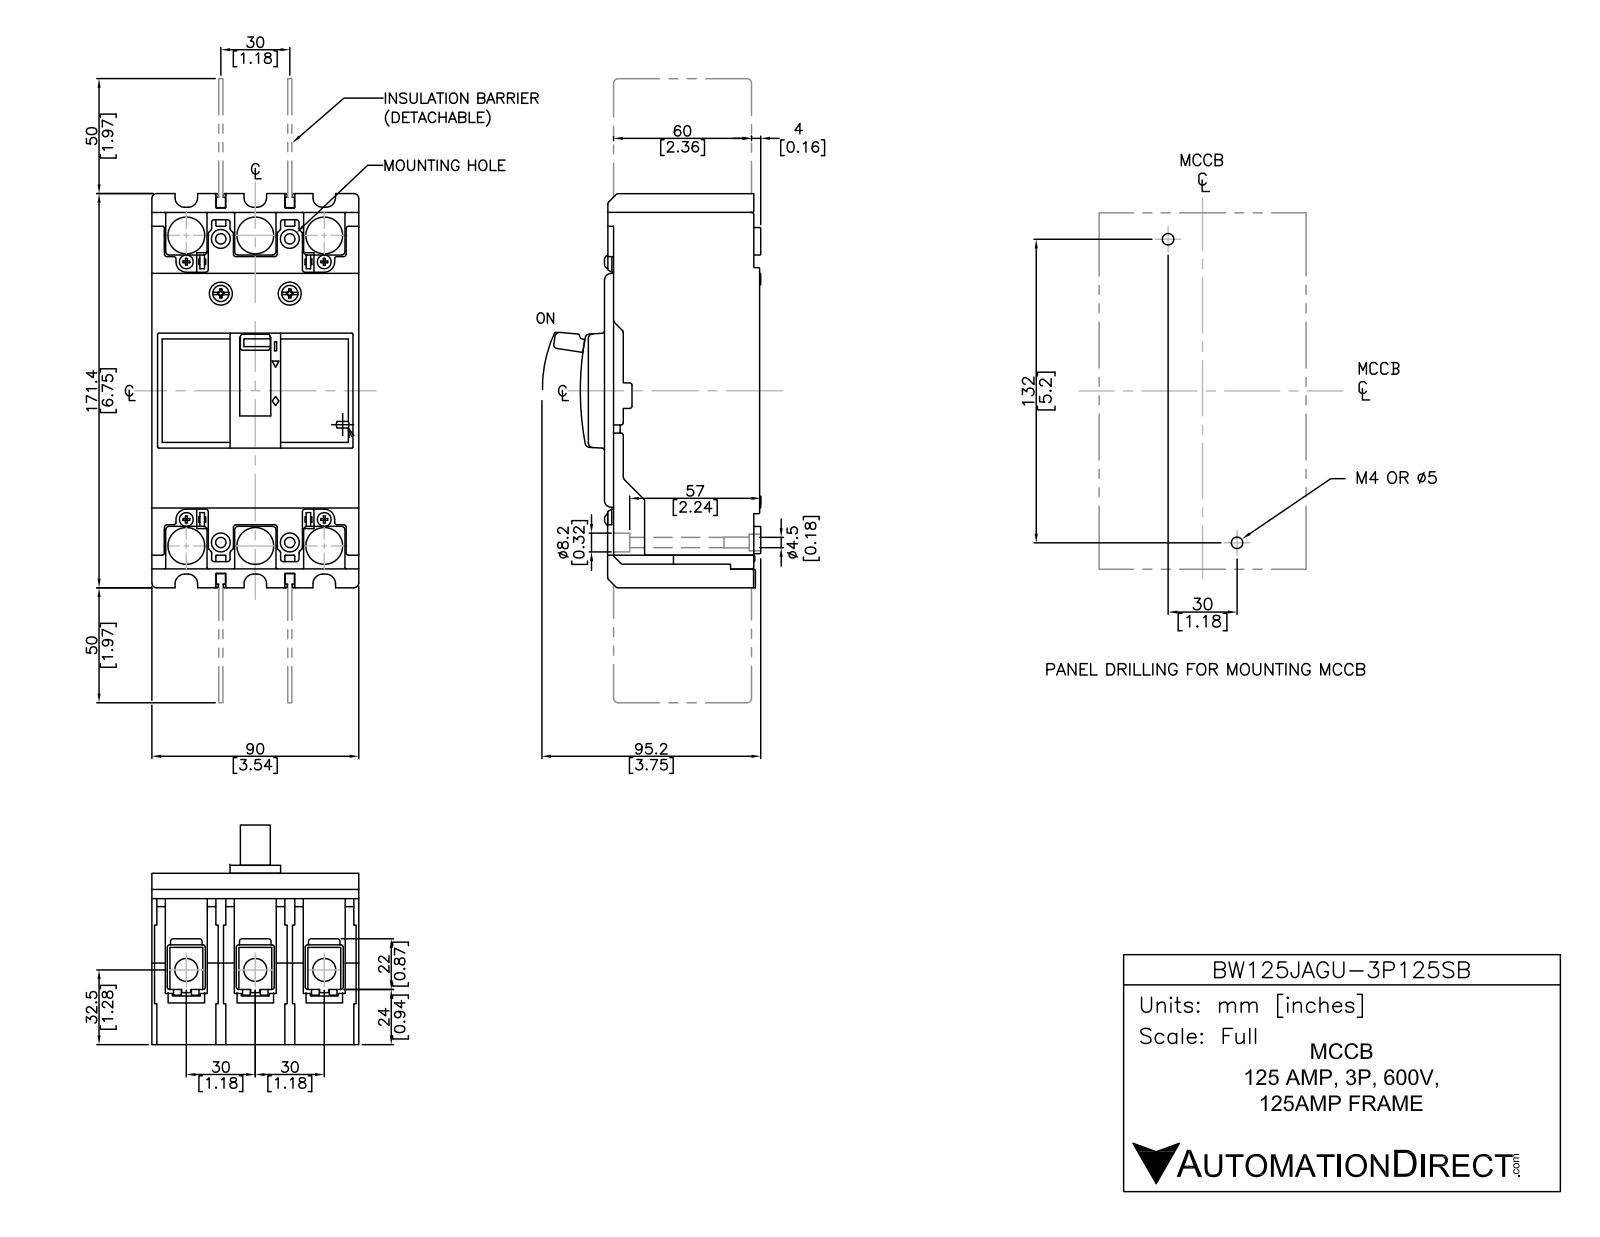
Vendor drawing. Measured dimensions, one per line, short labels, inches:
name: BW125JAGU-3P125SB
written by: SolidWorks 2018 (AUTOMOTIVE_DESIGN)
unit: in
bodies: 14 solids, 452 faces (340 planar, 88 cylindrical, 24 other)
size: 10.197 × 3.602 × 3.543
volume: 57.4 in³; area: 230.3 in²
holes: 6× ⌀0.315, 4× ⌀0.177, 4× ⌀0.323
bosses: 6× ⌀0.472
rounds: 12× R0.157, 6× R0.079, 6× R0.118
face distances: 1.181, 1.11, 1.252, 2.291, 2.433, 0.142, 3.543, 0.236, 2.402, 1.039
hole spacings: 0.593, 5.289, 1.181, 1.772, 5.444, 5.546, 5.315, 2.362
